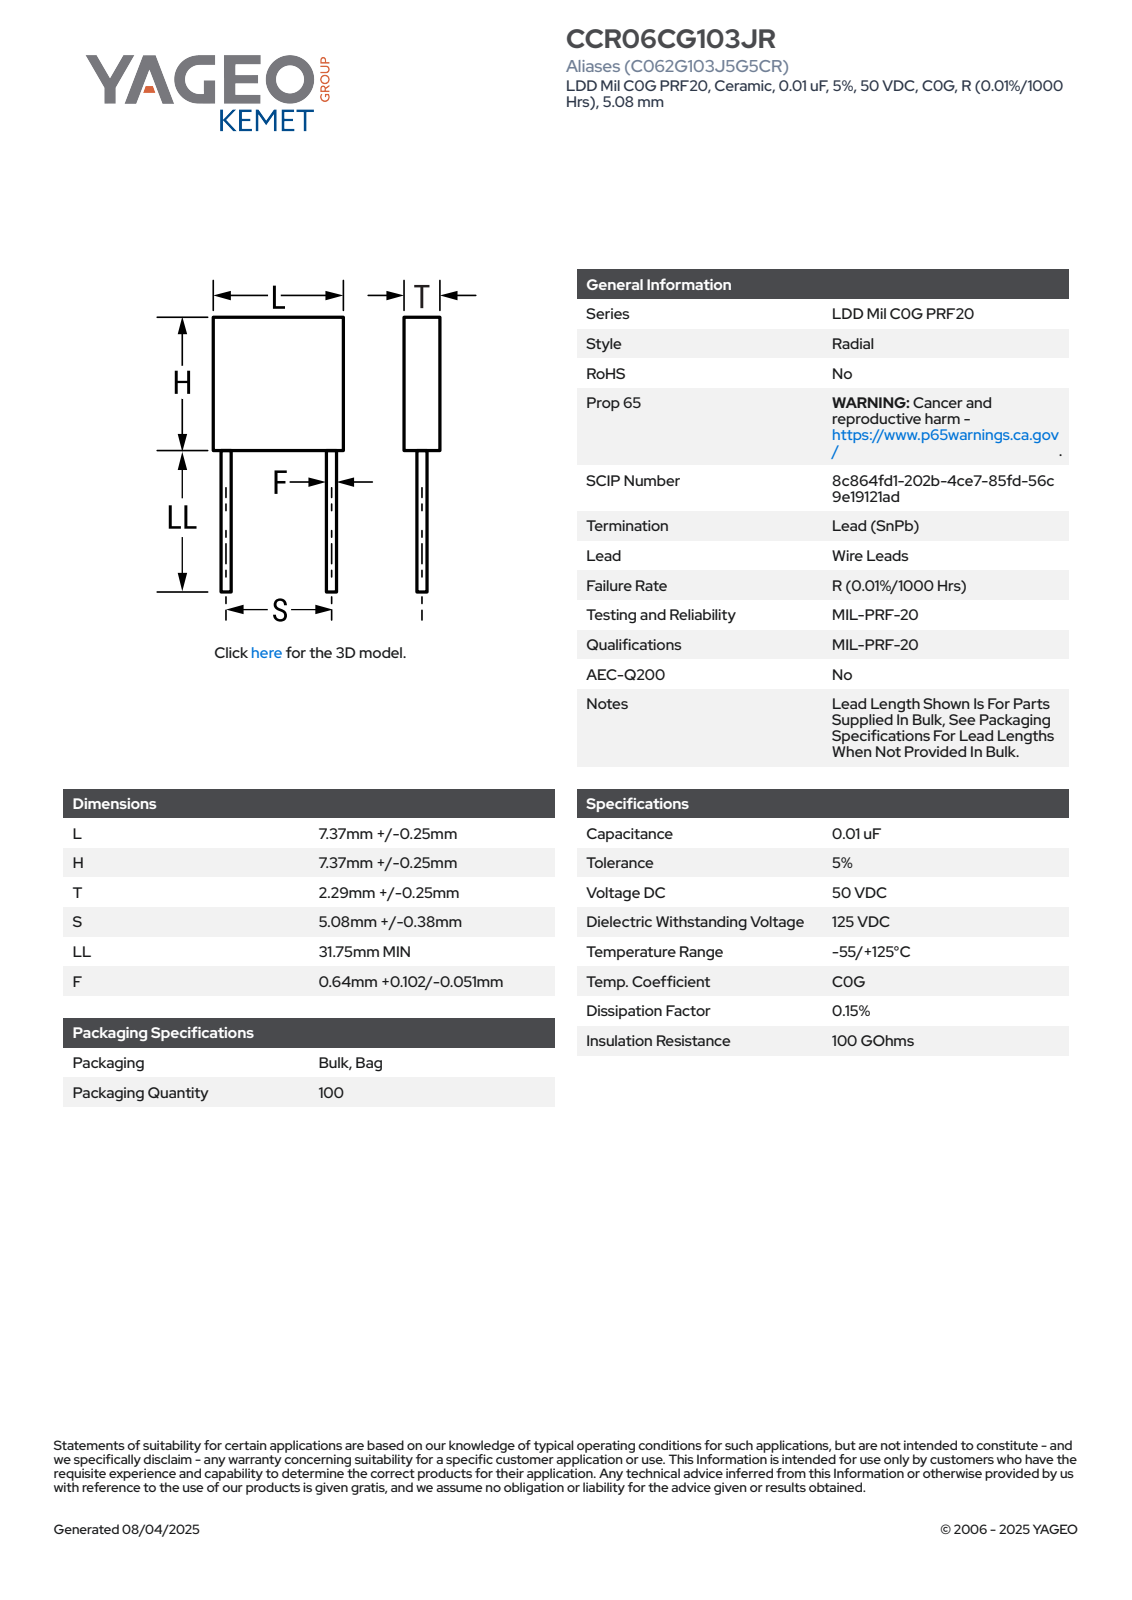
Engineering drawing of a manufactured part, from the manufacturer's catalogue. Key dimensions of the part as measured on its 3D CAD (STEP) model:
Part name (STEP PRODUCT): CCRM_ST_C062_L7.62H7.62T2.54S5.08LL31.75F0.742
STEP written by: SolidWorks 2014 (AUTOMOTIVE_DESIGN)
Units: millimetres
Bodies: 4 solids, 69 faces (65 planar, 4 cylindrical, 0 other)
Overall size (bounding box): 39.37 × 7.62 × 2.54
Volume: 175 mm³ · Surface area: 351 mm²
Round bosses / shafts (diameter × count): ⌀0.74 ×2
Main face-to-face distances: 2.54, 7.62, 31.75, 39.37, 3.19, 4.43, 36.18, 34.94, 1.24, 0.34
